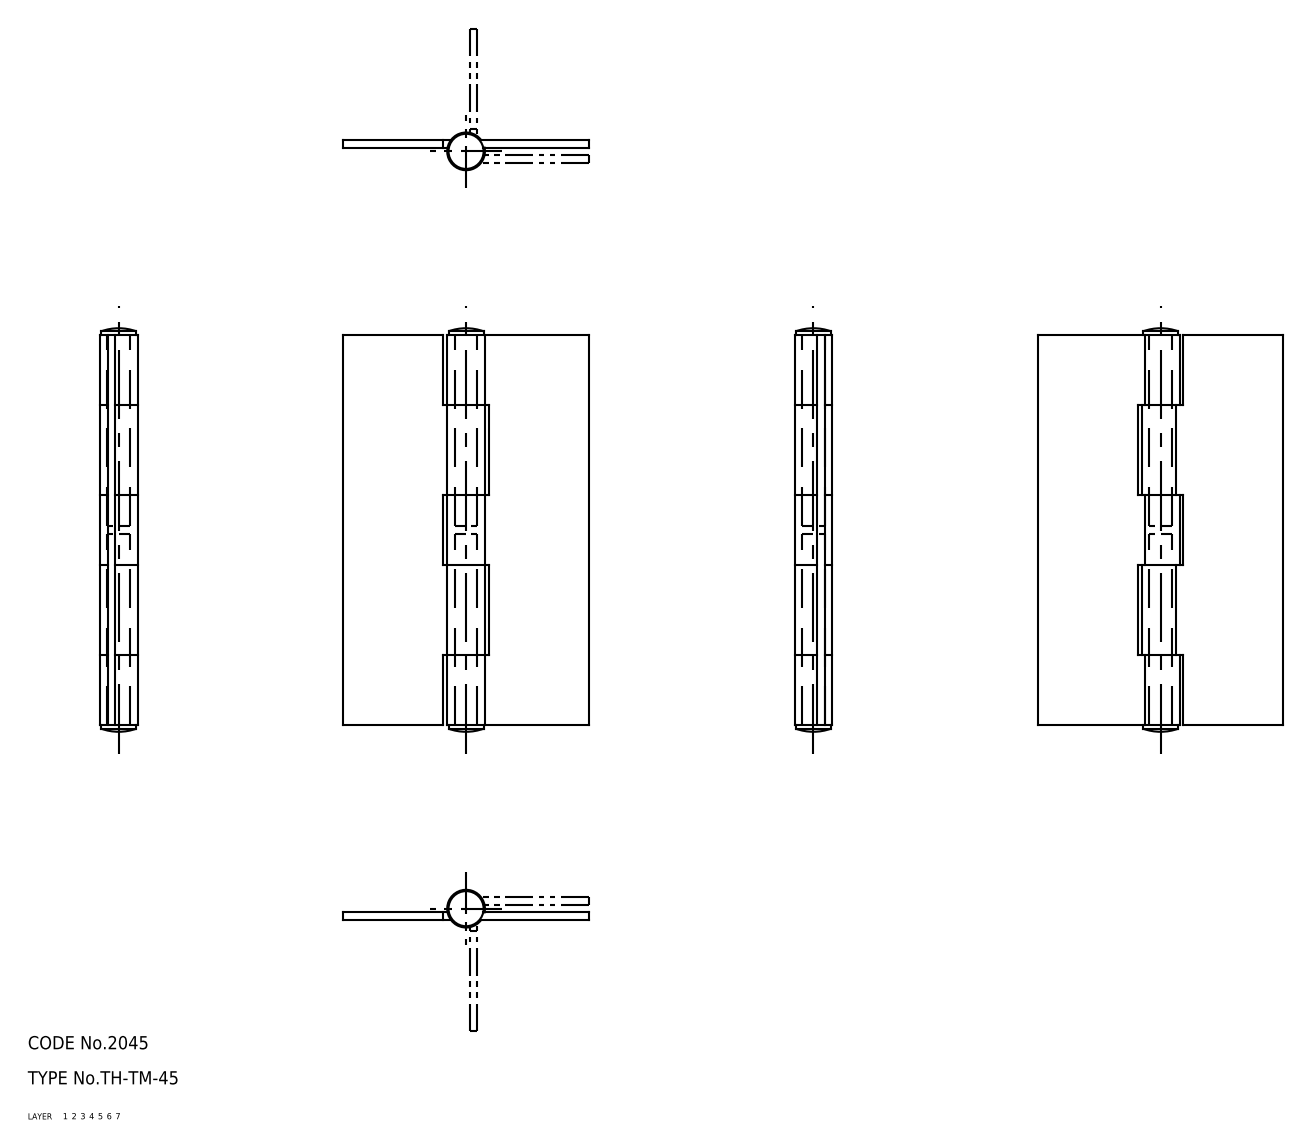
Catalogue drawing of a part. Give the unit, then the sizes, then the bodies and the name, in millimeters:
Units: millimetres
Overall size (bounding box): 92 × 56 × 8.6
Volume: 12 309 mm³ · Surface area: 14 984 mm²
Bodies: 4 solids, 52 faces (0 planar, 0 cylindrical, 52 other)
Part name (STEP PRODUCT): 67111615; 67111628; 67111641; 67111654
STEP written by: CADfix (AUTOMOTIVE_DESIGN)
